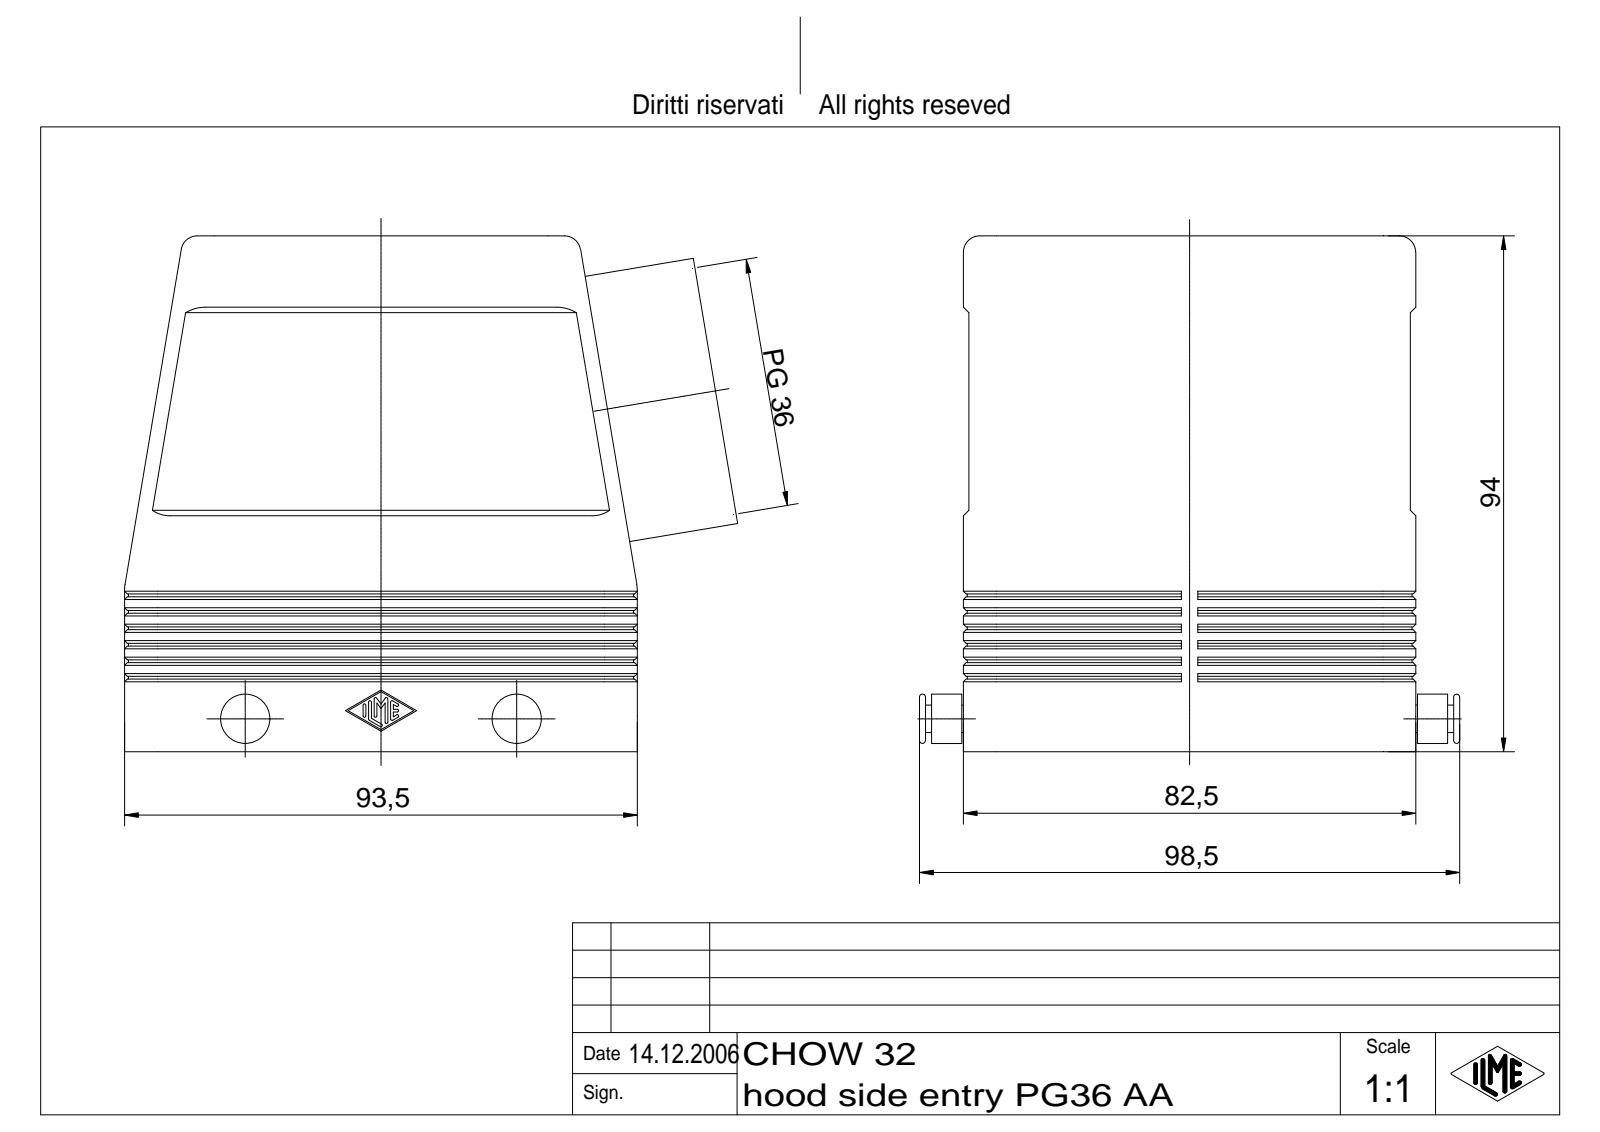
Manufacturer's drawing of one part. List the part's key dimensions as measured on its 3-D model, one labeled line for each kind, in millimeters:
Part name (STEP PRODUCT): CHOW 32
STEP written by: Autodesk Inventor 7 (AUTOMOTIVE_DESIGN)
Units: millimetres
Bodies: 1 solid, 613 faces (207 planar, 158 cylindrical, 248 other)
Overall size (bounding box): 111.78 × 98.5 × 94
Volume: 147 552 mm³ · Surface area: 79 748 mm²
Round holes (diameter × count): ⌀2.46 ×4, ⌀3.5 ×4, ⌀43.48 ×1, ⌀45.48 ×1
Round bosses / shafts (diameter × count): ⌀9 ×2, ⌀5 ×2, ⌀49 ×1
Partial cylindrical surfaces — rounded edges, fillets, slot ends (radius × count): R0.25 ×14, R2 ×12, R6 ×10, R3 ×4, R5.3 ×2
Main face-to-face distances: 4, 78.5, 74.5, 82.5, 3, 11, 1, 77.5, 81.5, 71.5
Hole centre spacings: 27, 77.5, 82.07
